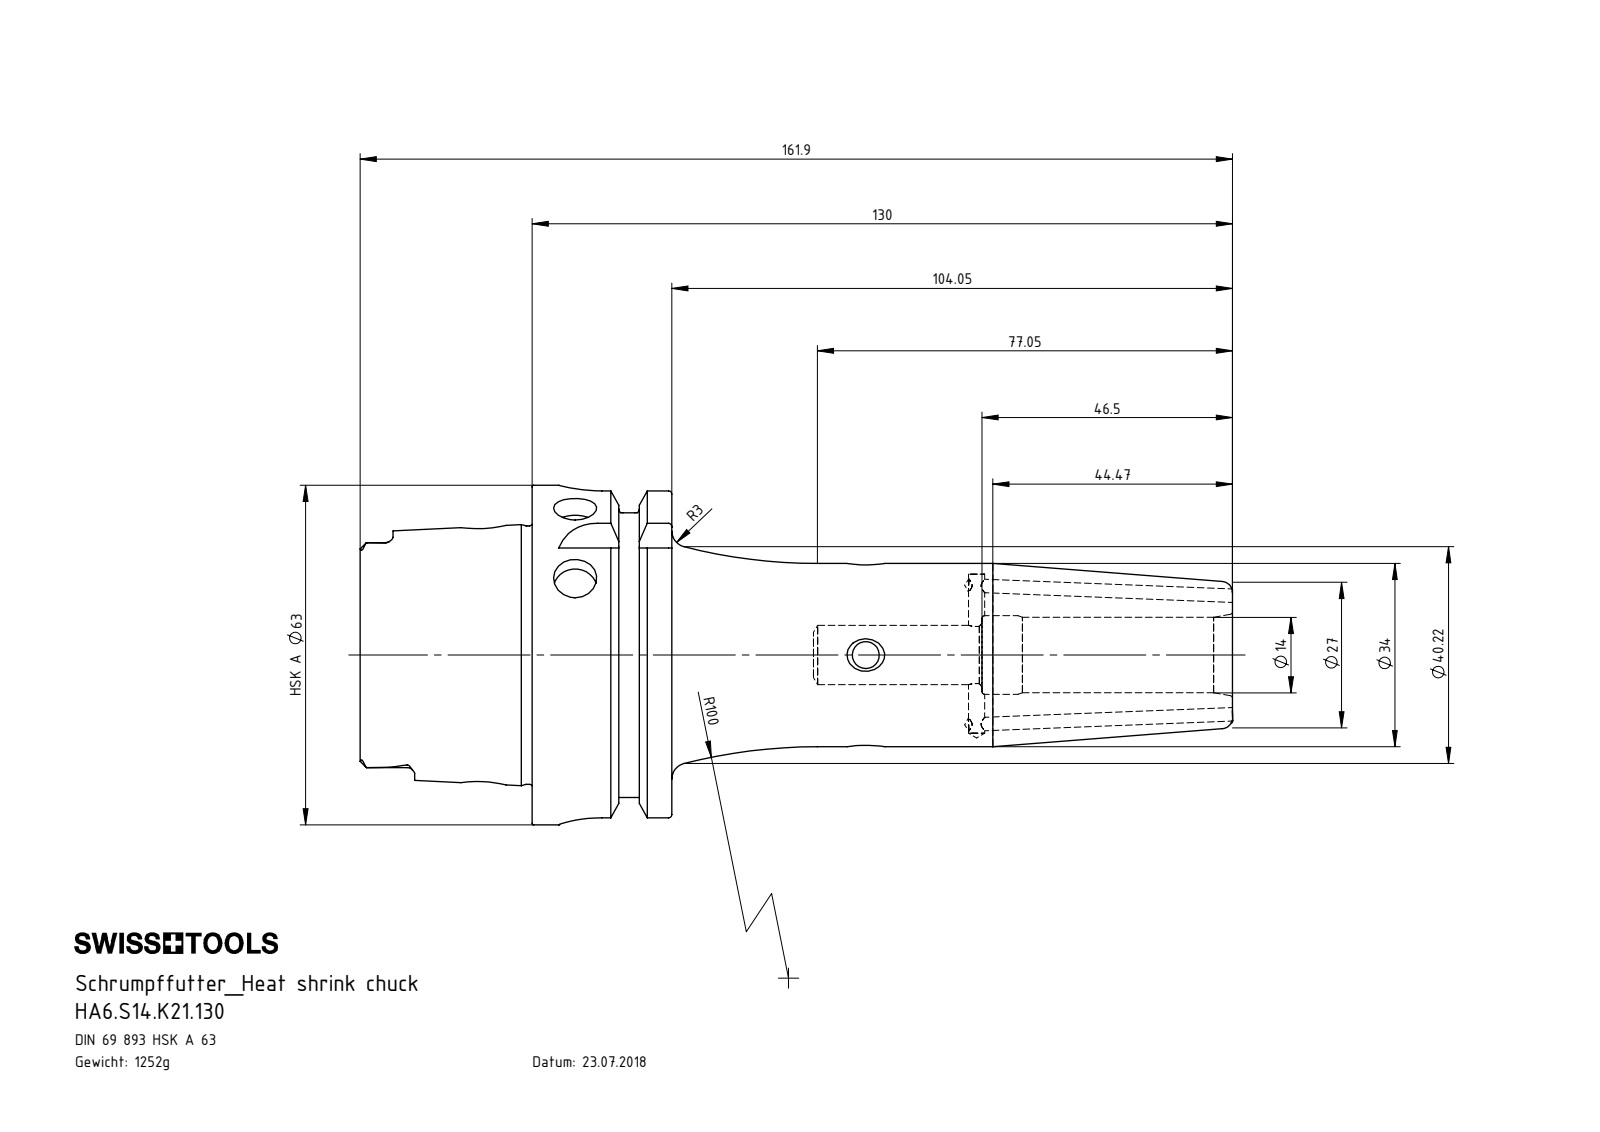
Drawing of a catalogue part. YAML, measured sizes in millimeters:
part_name: "HA6-S14.K21.130; ERU-AN4.K01.020_A; ERU-CJ2.001.006; HA6-S14.K21.130_C_Fertigbearbeitung"
step_written_by: "SolidWorks 2012 (CONFIG_CONTROL_DESIGN)"
units: millimeters
bodies: {solids: 4, faces: 312, planar: 102, cylindrical: 85, other: 125}
overall_size: [161.98, 63, 63]
volume: 159504
surface_area: 38786
round_holes:
  - {diameter: 5, count: 3}
  - {diameter: 2.5, count: 2}
  - {diameter: 8, count: 2}
  - {diameter: 3, count: 1}
  - {diameter: 7.5, count: 1}
  - {diameter: 8.4, count: 1}
  - {diameter: 10, count: 1}
  - {diameter: 11, count: 1}
  - {diameter: 14, count: 1}
  - {diameter: 14.6, count: 1}
  - {diameter: 17, count: 1}
  - {diameter: 19, count: 1}
round_bosses_or_shafts:
  - {diameter: 3, count: 2}
  - {diameter: 63, count: 1}
  - {diameter: 54.95, count: 1}
  - {diameter: 47.94, count: 1}
  - {diameter: 10, count: 1}
  - {diameter: 9, count: 1}
partial_cylinders:
  - {radius: 1.4, count: 6}
  - {radius: 2.88, count: 4}
  - {radius: 8, count: 4}
face_to_face_distances: [25.95, 16, 9.95, 31.9, 41.85, 57.85, 52.8, 21.8, 11.85, 53.7]
hole_center_spacings: [20.55, 54.95, 70.95, 91.5]
